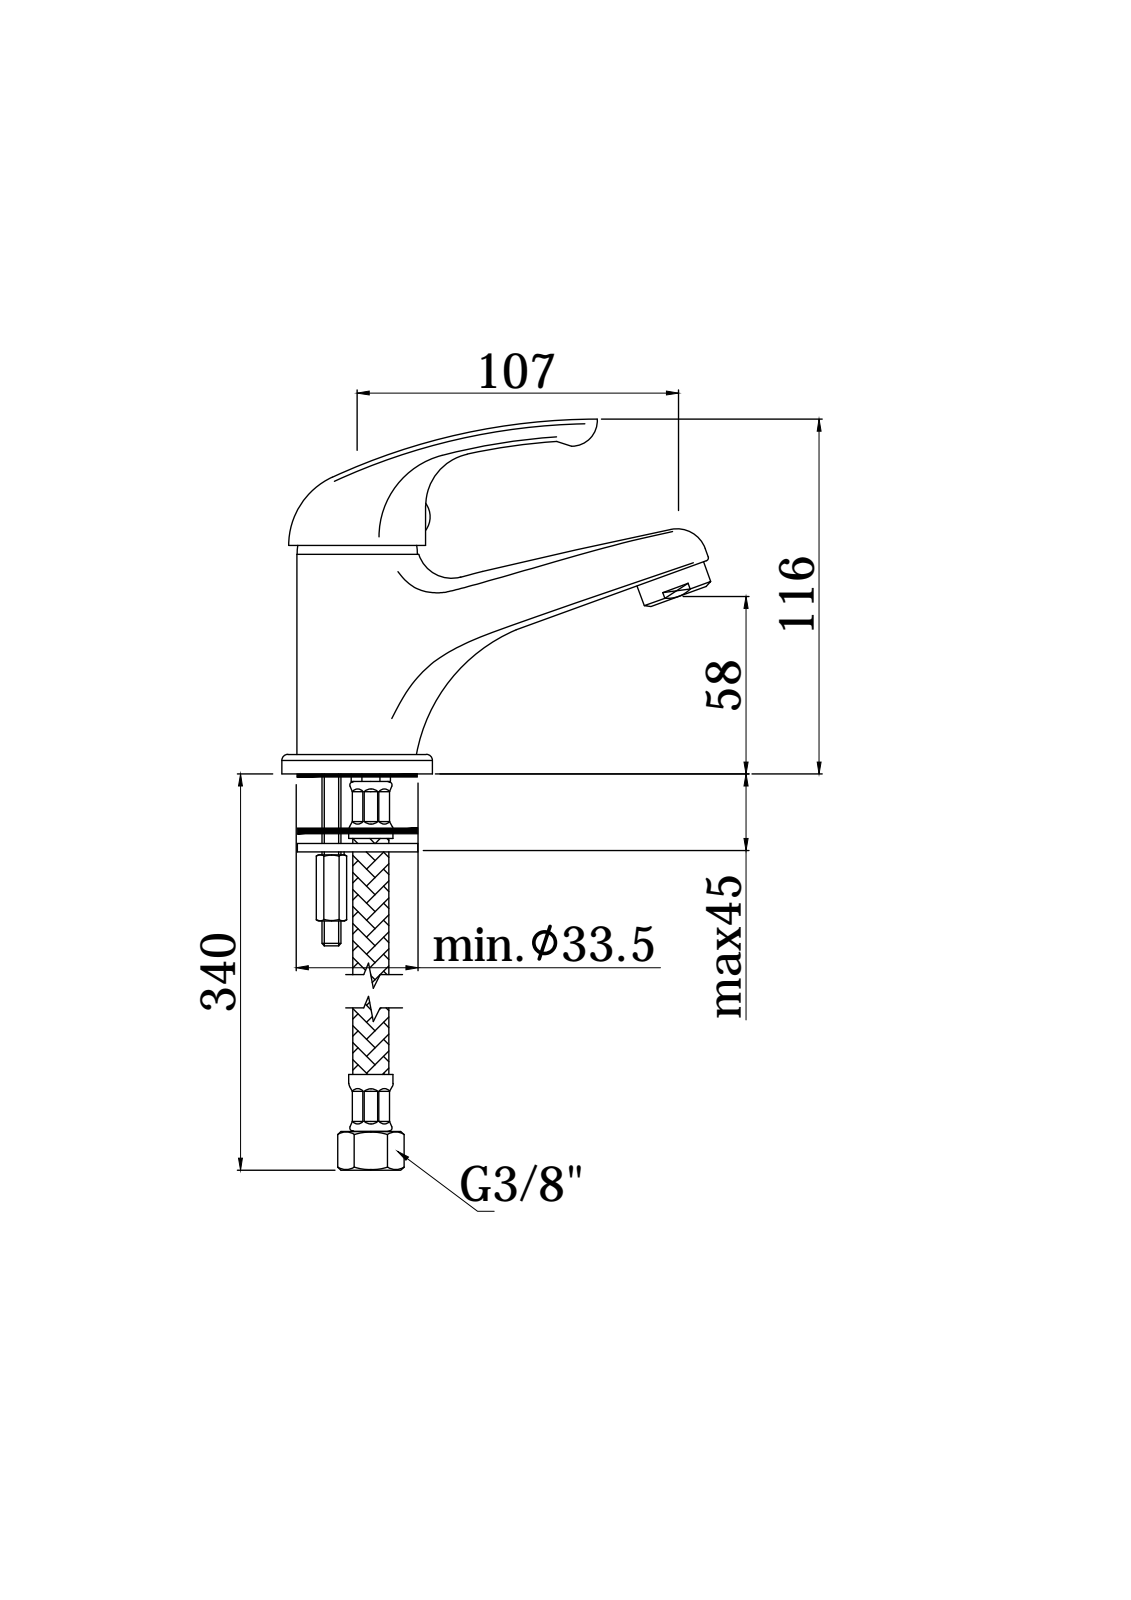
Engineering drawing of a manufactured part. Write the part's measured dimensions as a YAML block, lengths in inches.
part_name: "APM3071CR"
step_written_by: "CREO PARAMETRIC BY PTC INC, 2020044 (CONFIG_CONTROL_DESIGN)"
units: inches
bodies: {solids: 2, faces: 2784, planar: 2041, cylindrical: 364, other: 379}
overall_size: [5.927, 4.705, 2.047]
volume: 7.585
surface_area: 133.5
round_holes:
  - {diameter: 0.354, count: 5}
  - {diameter: 0.197, count: 3}
  - {diameter: 0.472, count: 3}
  - {diameter: 0.157, count: 2}
  - {diameter: 0.276, count: 2}
  - {diameter: 0.315, count: 2}
  - {diameter: 0.433, count: 2}
  - {diameter: 0.098, count: 1}
  - {diameter: 0.13, count: 1}
  - {diameter: 0.236, count: 1}
  - {diameter: 0.63, count: 1}
  - {diameter: 0.669, count: 1}
round_bosses_or_shafts:
  - {diameter: 0.315, count: 4}
  - {diameter: 2.047, count: 1}
  - {diameter: 1.752, count: 1}
  - {diameter: 1.677, count: 1}
  - {diameter: 1.488, count: 1}
  - {diameter: 1.378, count: 1}
  - {diameter: 1.37, count: 1}
  - {diameter: 1.331, count: 1}
partial_cylinders:
  - {radius: 0.02, count: 43}
  - {radius: 0.039, count: 25}
  - {radius: 0.006, count: 11}
  - {radius: 0.012, count: 9}
  - {radius: 0.059, count: 8}
  - {radius: 0.276, count: 4}
  - {radius: 0.157, count: 2}
  - {radius: 0.177, count: 2}
face_to_face_distances: [0.138, 0.098, 0.02, 0.118, 0.059, 0.079, 0.039, 0.453, 0.197, 0.374]
hole_center_spacings: [0.535, 0.02, 0.028, 0.044, 0.335, 0.339, 0.355, 0.44]
